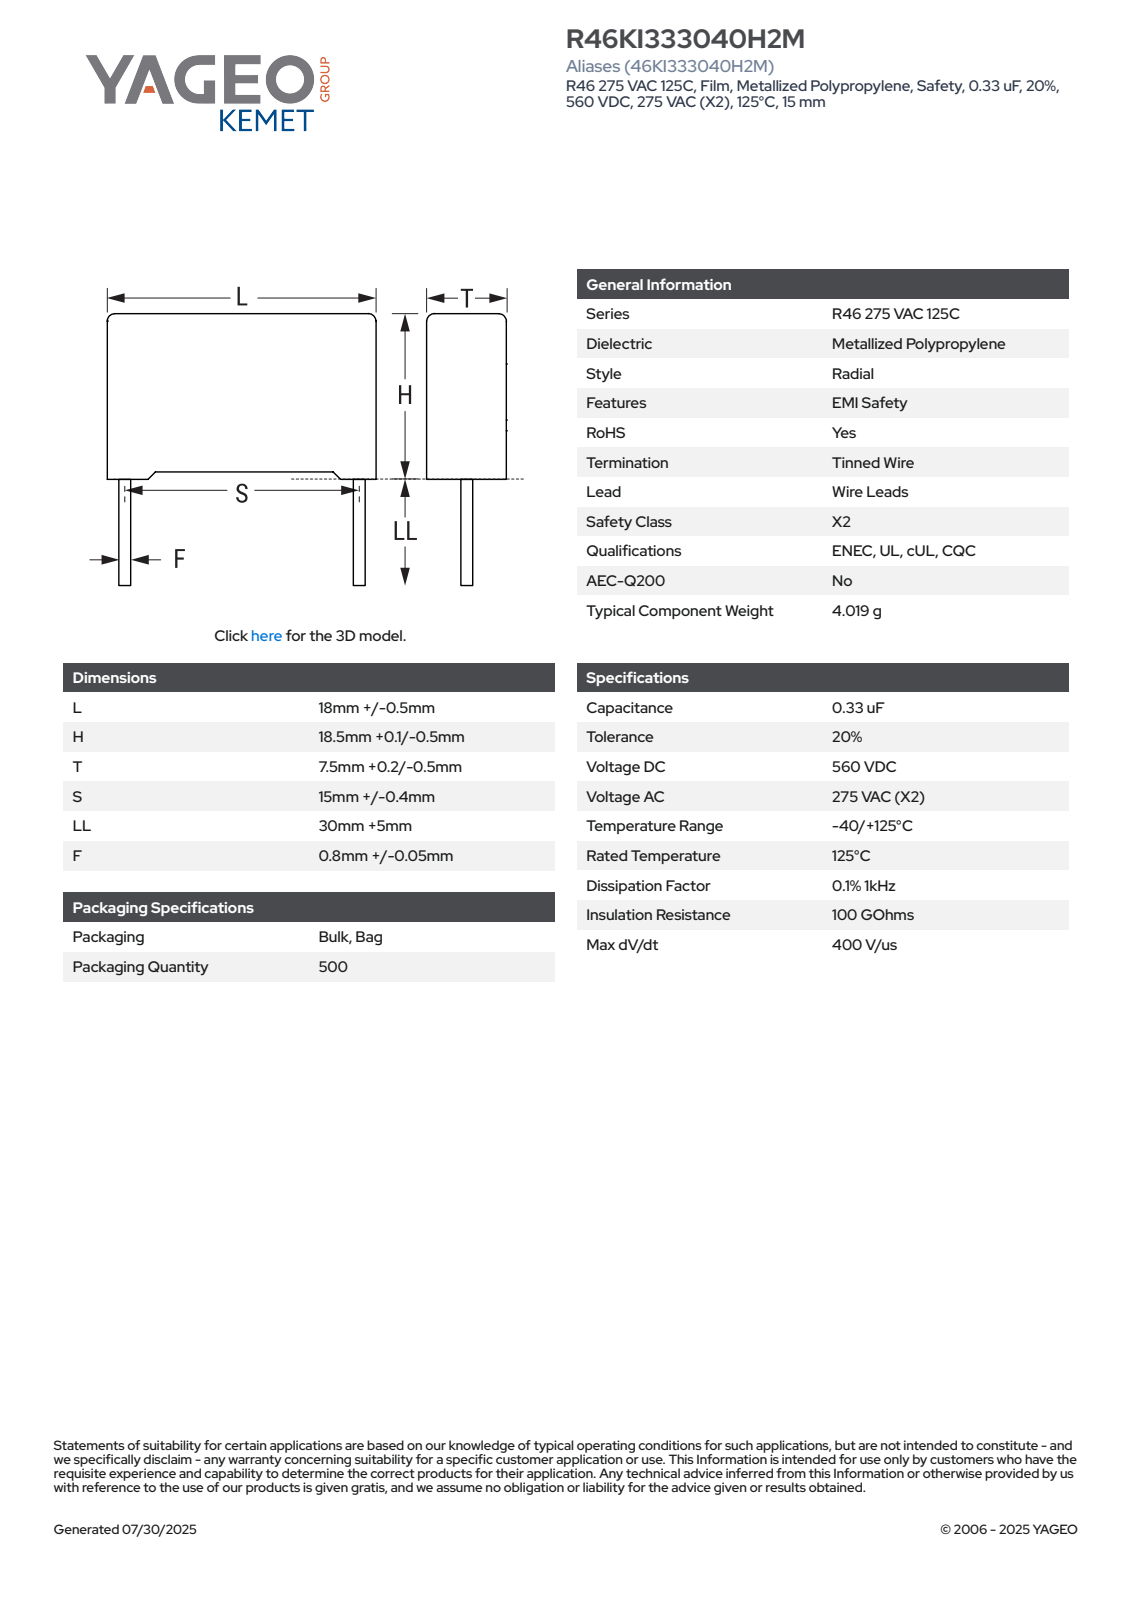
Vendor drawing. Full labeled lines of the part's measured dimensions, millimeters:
Part name (STEP PRODUCT): CFR_RB2_18X18.5X7.5_L18.5H18.6T7.7S15LL35F0.85
STEP written by: SolidWorks 2021 (AUTOMOTIVE_DESIGN)
Units: millimetres
Bodies: 4 solids, 85 faces (77 planar, 8 cylindrical, 0 other)
Overall size (bounding box): 53.6 × 18.5 × 7.71
Volume: 2 595 mm³ · Surface area: 1 472 mm²
Round bosses / shafts (diameter × count): ⌀0.85 ×2
Partial cylindrical surfaces — rounded edges, fillets, slot ends (radius × count): R0.5 ×4
Main face-to-face distances: 7.7, 18.5, 17.85, 0.62, 0.75, 18.6, 0.64, 17.96, 7.08, 17.88
